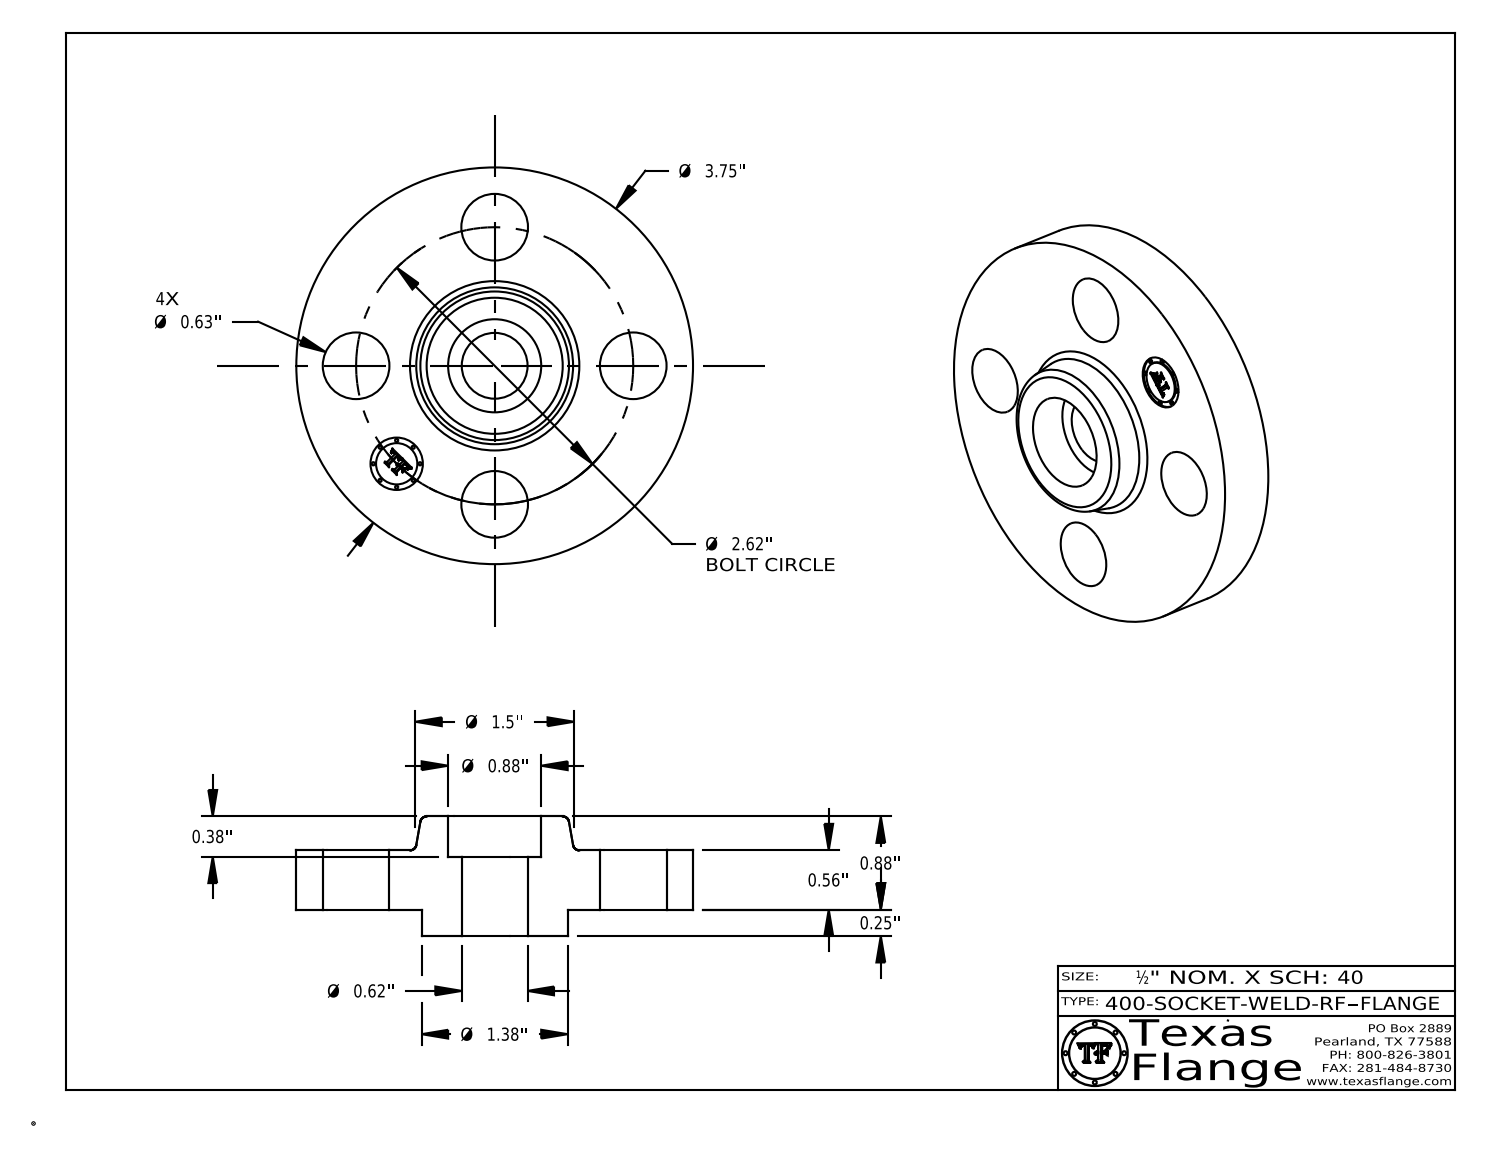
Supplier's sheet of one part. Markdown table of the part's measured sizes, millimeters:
| quantity | value |
| --- | --- |
| part name | 400-SOCKET-WELD-RF |
| STEP written by | CATIA V5 STEP AP214 (AUTOMOTIVE_DESIGN) |
| units | millimeters |
| bodies | 1 solid, 412 faces (370 planar, 36 cylindrical, 6 other) |
| overall size | 95.3 × 95.3 × 28.7 |
| volume | 97 090 mm³ |
| surface area | 22 440 mm² |
| round holes (diameter × count) | 16 × 4, 12.6 × 1, 15.8 × 1, 22.4 × 1 |
| round bosses / shafts (diameter × count) | 0.8 × 8, 95.3 × 1, 35.1 × 1, 9.9 × 1 |
| main face-to-face distances | 14.2, 6.4, 20.6, 28.7, 22.4, 8.1, 19.1, 12.7, 1.5, 9.7 |
| hole center spacings | 33.3, 47, 25.5, 61.5, 66.5, 33.3 |
